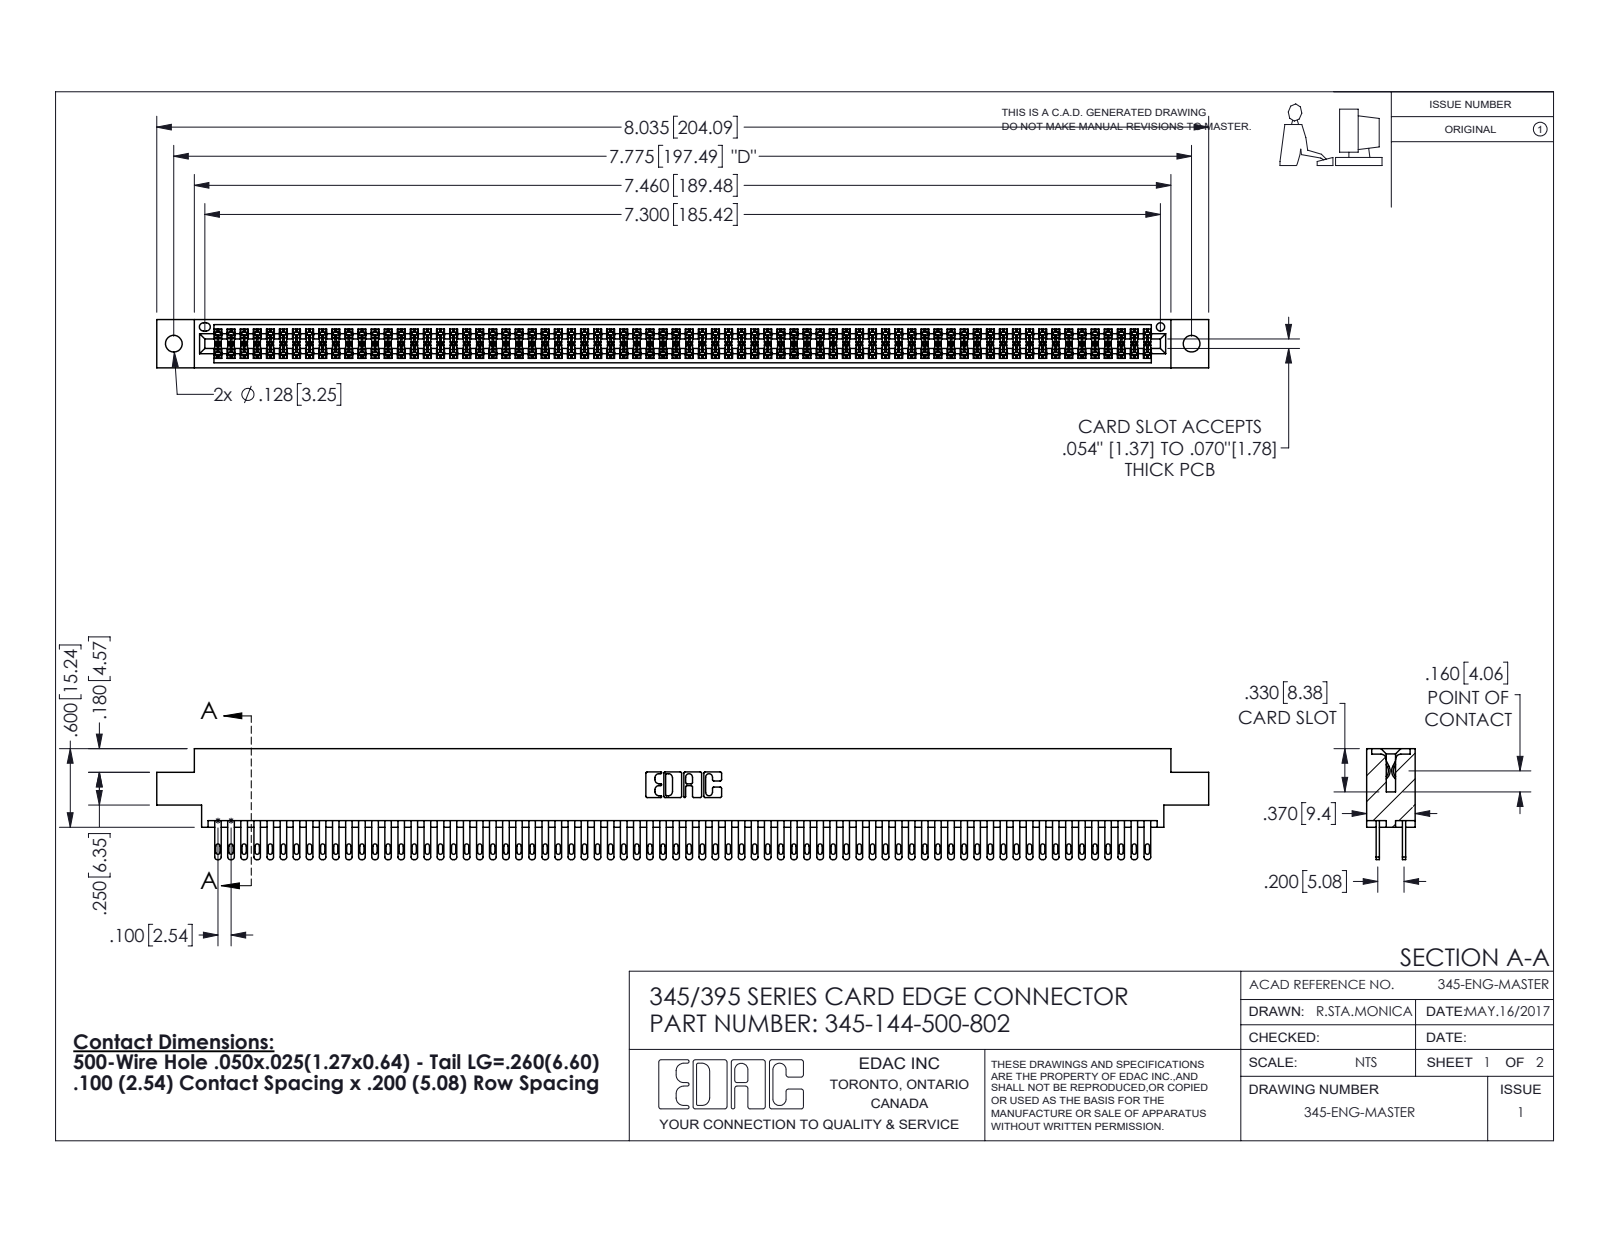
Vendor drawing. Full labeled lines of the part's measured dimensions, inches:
Part name (STEP PRODUCT): 345-144-500-802; 345 Part_0.170 Offset - 0.128 Dia; 345-292-001_345-293-100
STEP written by: SolidWorks 2016 (CONFIG_CONTROL_DESIGN)
Units: inches
Bodies: 145 solids, 6754 faces (3972 planar, 2782 cylindrical, 0 other)
Overall size (bounding box): 8.035 × 0.847 × 0.37
Volume: 1.245 in³ · Surface area: 49.7 in²
Round holes (diameter × count): ⌀0.128 ×2, ⌀0.064 ×1
Partial cylindrical surfaces — rounded edges, fillets, slot ends (radius × count): R0.006 ×216, R0.016 ×144, R0.02 ×144, R0.01 ×22, R0.007 ×6, R0.031 ×6, R0.026 ×3, R0.014 ×2
Main face-to-face distances: 0.072, 0.298, 0.2, 0.098, 0.272, 0.025, 0.37, 0.225, 0.175, 0.149
Hole centre spacings: 0.27, 7.539, 7.775
